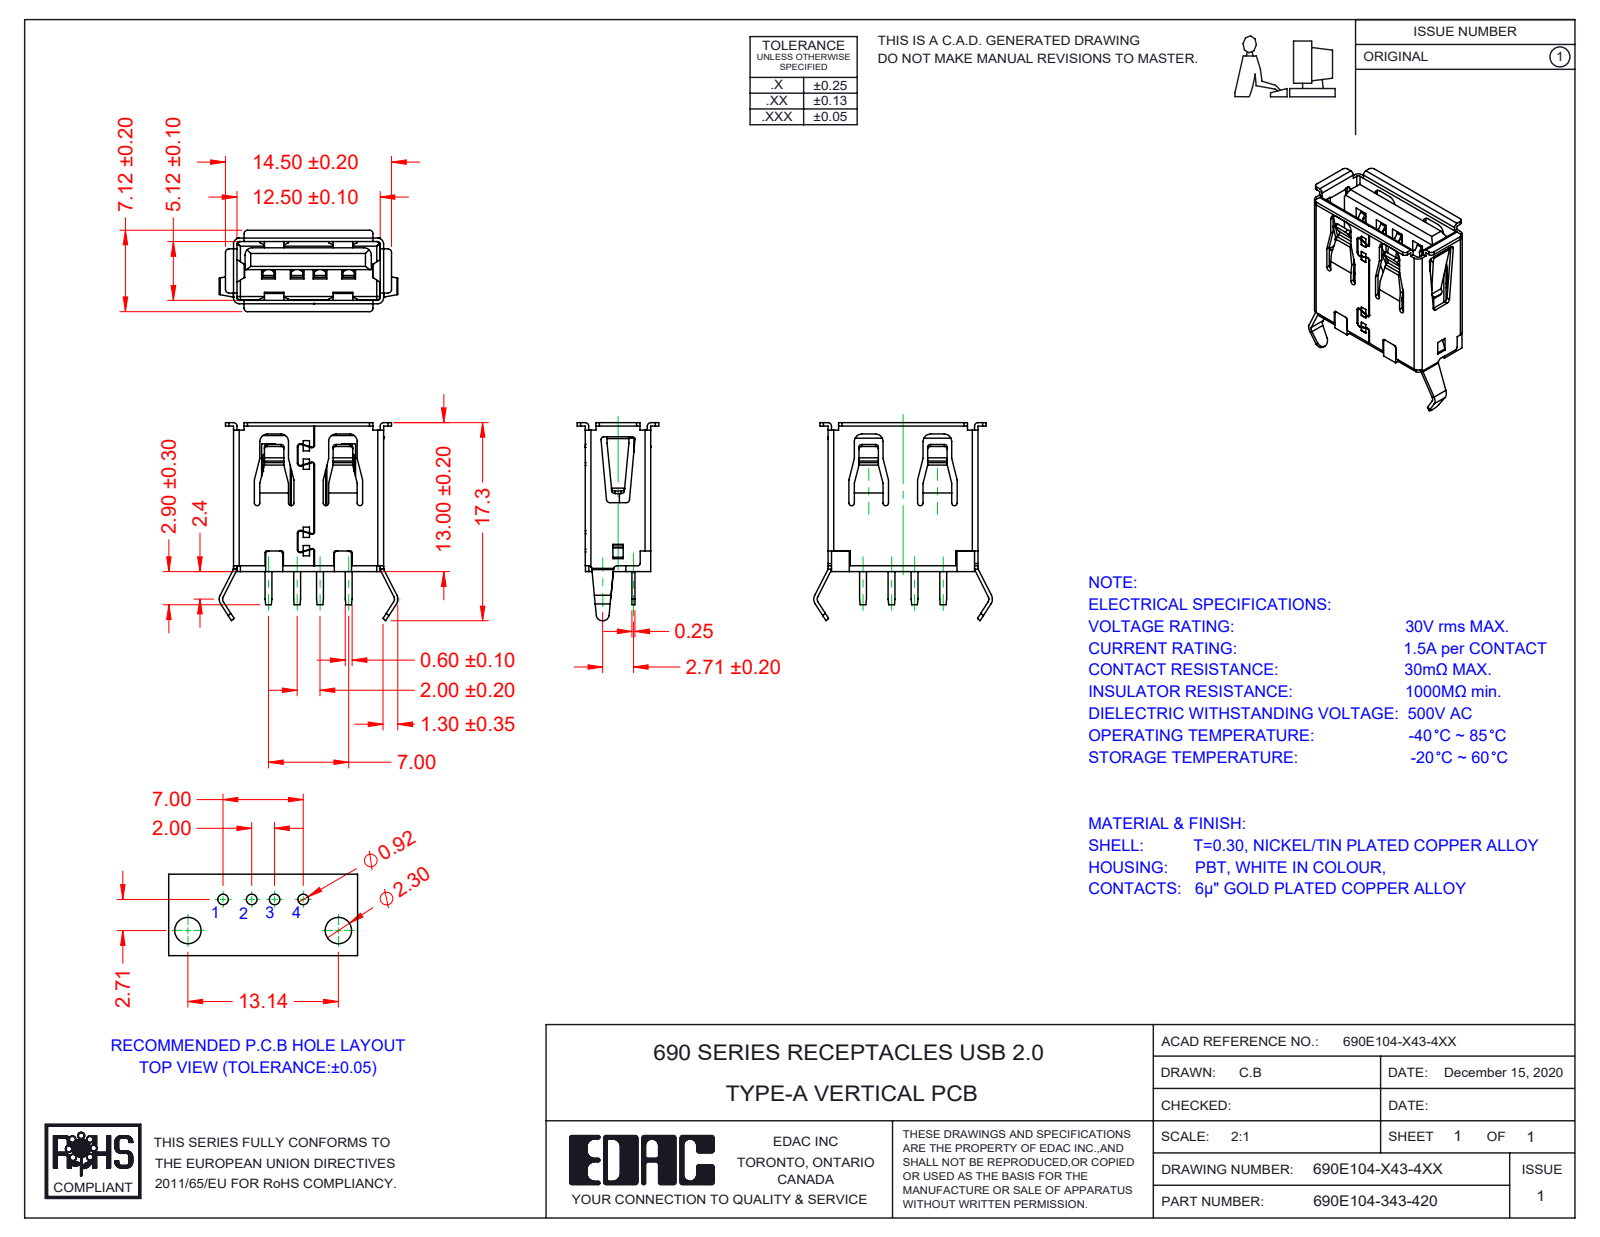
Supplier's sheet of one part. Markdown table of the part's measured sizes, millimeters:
| quantity | value |
| --- | --- |
| part name | Insulator 690E104-X43-4XX_White; 690E104-143-420; Contacts 690E104-X43-4XX; Shell 690E104-X43-4XX |
| STEP written by | SolidWorks 2020 (AUTOMOTIVE_DESIGN) |
| units | millimeters |
| bodies | 6 solids, 690 faces (491 planar, 194 cylindrical, 5 other) |
| overall size | 17.3 × 15.6 × 7.12 |
| volume | 462 mm³ |
| surface area | 1 764 mm² |
| partial cylindrical surfaces (radius × count) | 0.2 × 37, 0.3 × 33, 0.15 × 17, 0.25 × 14, 0.5 × 10, 0.24 × 4, 0.56 × 4, 0.65 × 4 |
| main face-to-face distances | 5.42, 5.72, 5.12, 1.39, 1.09, 4.03, 4.33, 12.8, 0.55, 4.5 |
